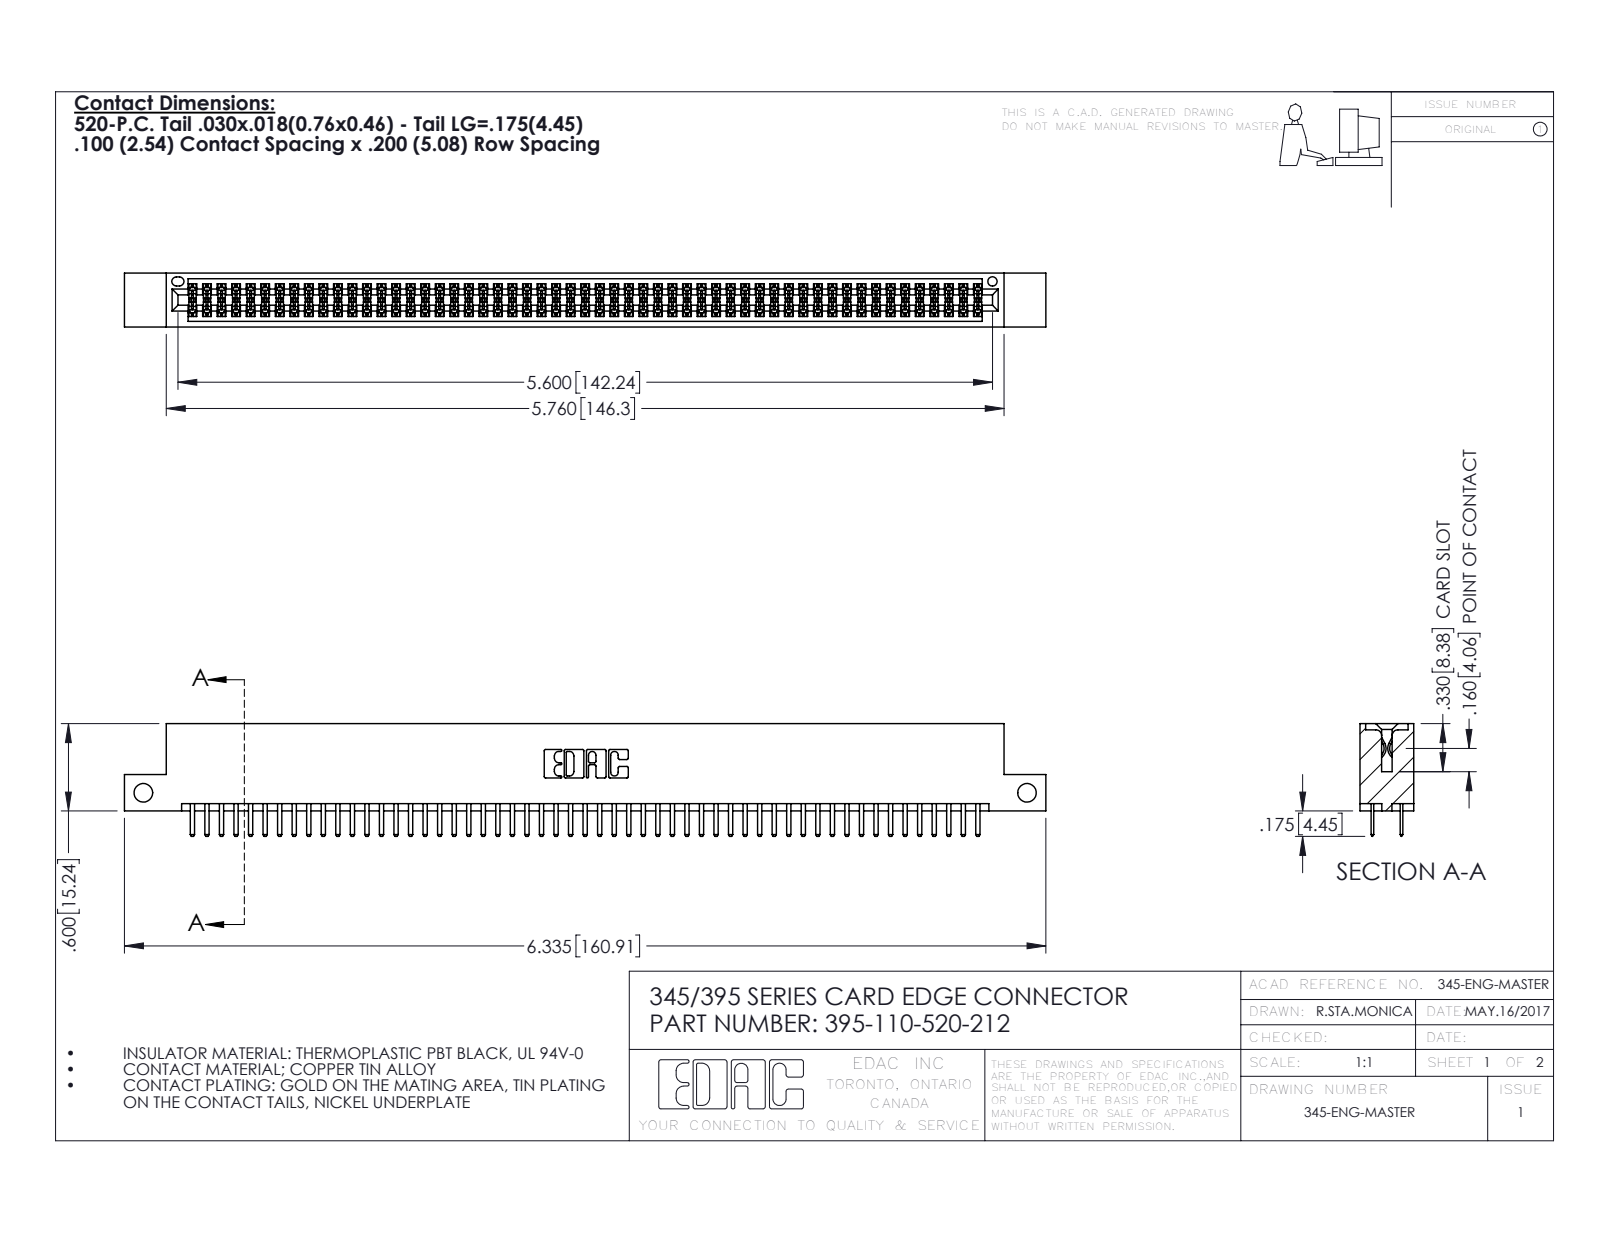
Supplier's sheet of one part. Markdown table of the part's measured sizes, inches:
| quantity | value |
| --- | --- |
| part name | 345-292-001_345-293-120; 345 Part_Flush Mounting Lugs - Side Mount; 395-110-520-212 |
| STEP written by | SolidWorks 2016 (CONFIG_CONTROL_DESIGN) |
| units | inches |
| bodies | 111 solids, 6066 faces (3930 planar, 2136 cylindrical, 0 other) |
| overall size | 6.335 × 0.775 × 0.37 |
| volume | 0.953 in³ |
| surface area | 35.8 in² |
| round holes (diameter × count) | 0.128 × 2, 0.064 × 1 |
| partial cylindrical surfaces (radius × count) | 0.006 × 165, 0.01 × 114, 0.01 × 22, 0.007 × 6, 0.031 × 6, 0.026 × 3, 0.014 × 2, 0.019 × 2 |
| main face-to-face distances | 0.298, 0.072, 0.2, 0.37, 0.098, 0.272, 0.025, 0.225, 0.022, 0.072 |
| hole center spacings | 6.075 |
